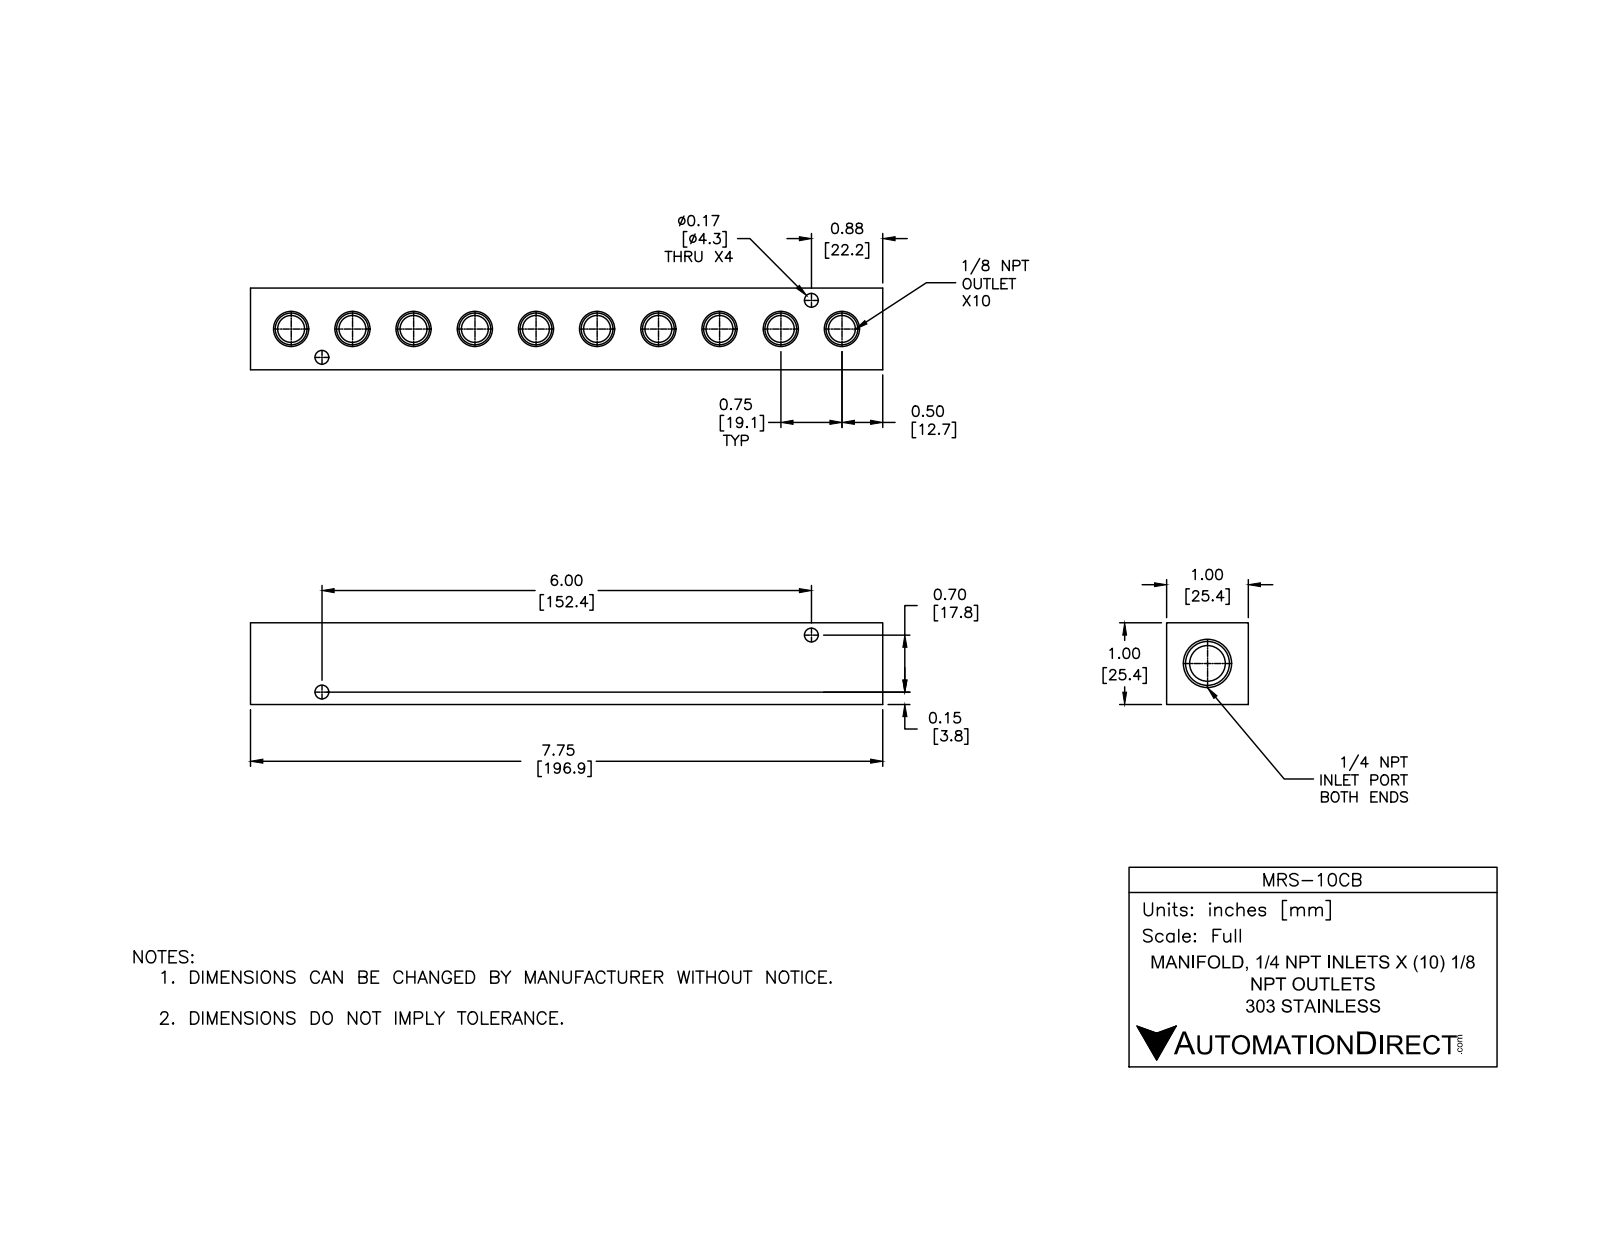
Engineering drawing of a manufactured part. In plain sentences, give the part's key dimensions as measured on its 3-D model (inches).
The part is named "MRS-10CB". Its 3-D file was written by "SolidWorks 2015 (CONFIG_CONTROL_DESIGN)". It is 1 solid with 103 faces: 18 planar, 37 cylindrical and 48 other. Overall it measures 7.75 by 1 by 1 inches. Its volume is 6.083 cubic inches and its surface area 47.01 square inches. Round holes: 8 of diameter 0.332, 4 of diameter 0.17, 1 of diameter 0.438. Partial cylindrical surfaces (rounded edges, fillets, slot ends): 2 of radius 0.166. The main face-to-face distances are 1, 7.75, 0.73, 0.27, 0.39, 7.36, 6.97. The hole center spacings are 0.75, 1.5, 2.25, 3, 0.513, 1.178, 3.75, 4.887.
